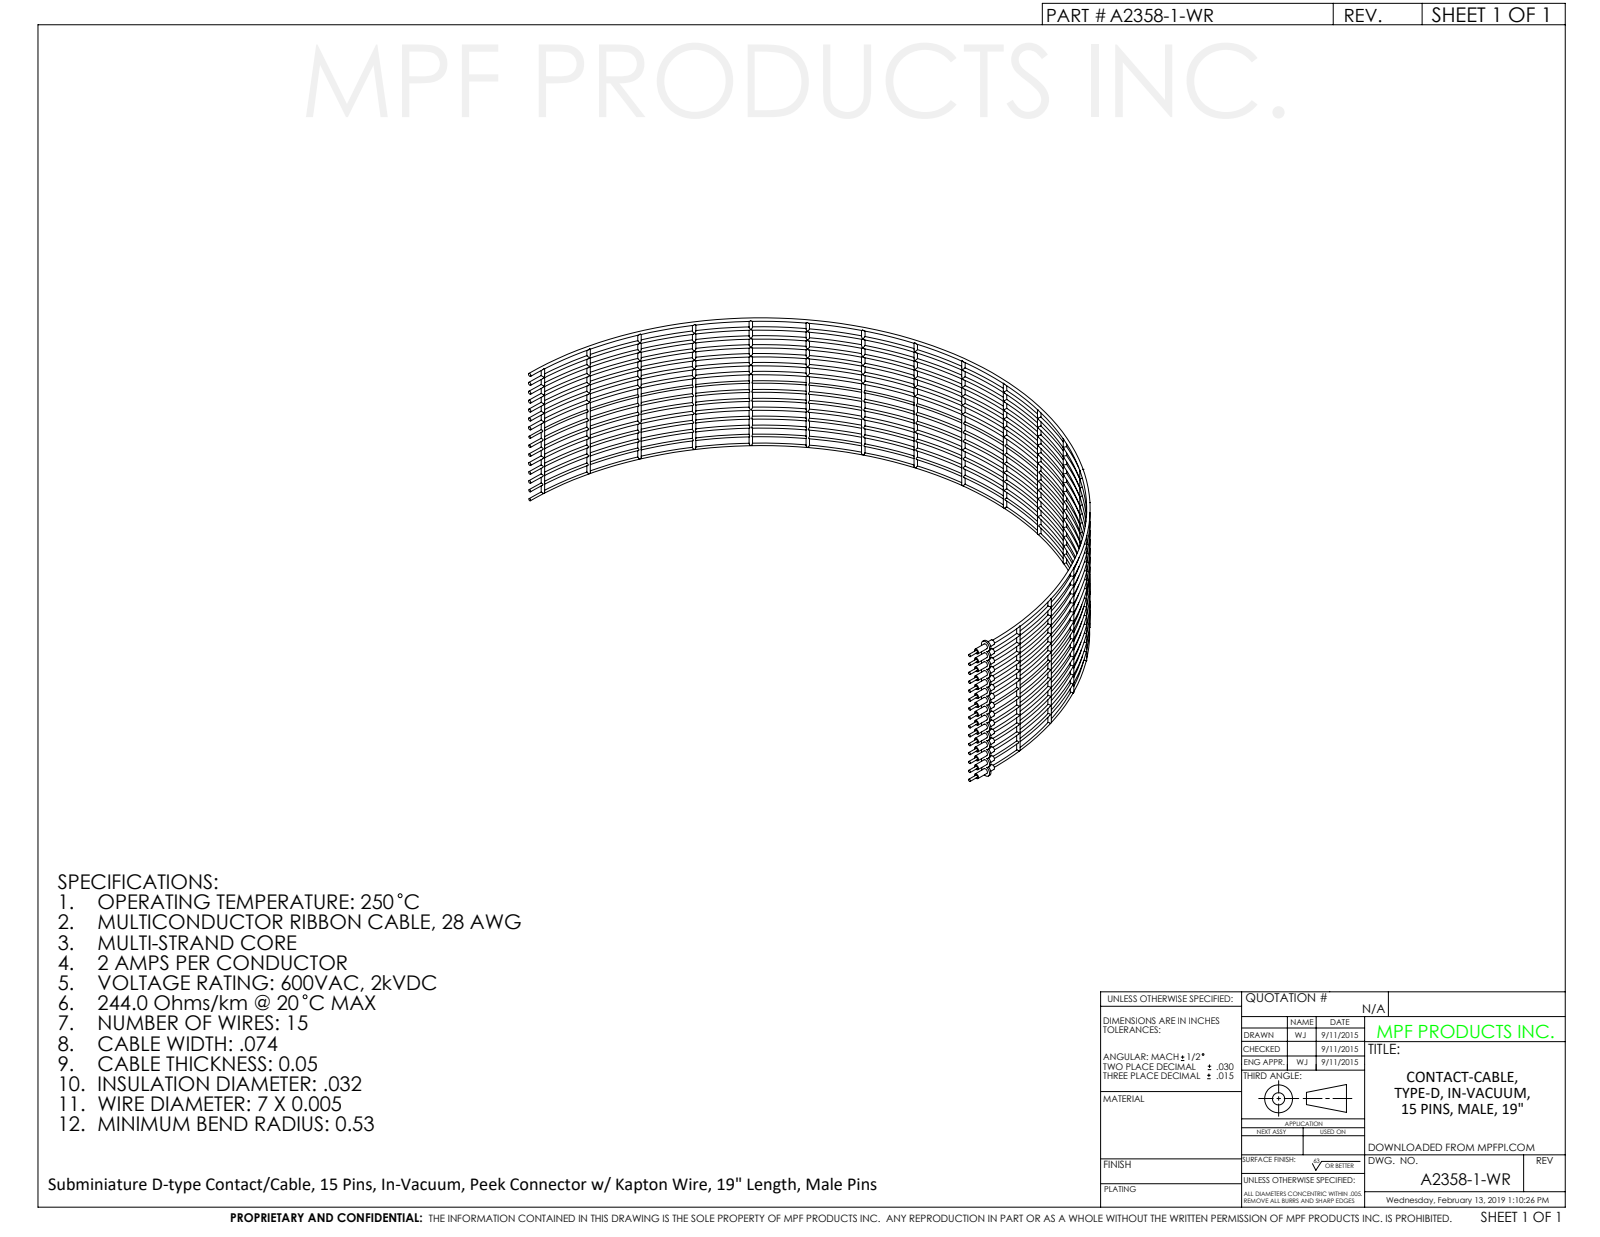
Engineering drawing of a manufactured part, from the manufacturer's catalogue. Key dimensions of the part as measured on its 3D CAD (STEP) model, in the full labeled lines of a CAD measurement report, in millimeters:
Part name (STEP PRODUCT): A2358-1-WR
STEP written by: SolidWorks 2012 (CONFIG_CONTROL_DESIGN)
Units: millimetres
Bodies: 1 solid, 1049 faces (99 planar, 386 cylindrical, 564 other)
Overall size (bounding box): 154.1 × 84.2 × 38.2
Volume: 1 900 mm³ · Surface area: 9 781 mm²
Round bosses / shafts (diameter × count): ⌀0.8 ×18, ⌀1.3 ×15, ⌀0.6 ×15, ⌀2.7 ×14
Partial cylindrical surfaces — rounded edges, fillets, slot ends (radius × count): R1.3 ×1
Main face-to-face distances: 0.5, 1.9, 2.3, 5.3, 3.4, 2.9, 7.6, 5.7, 5.3, 2.3
